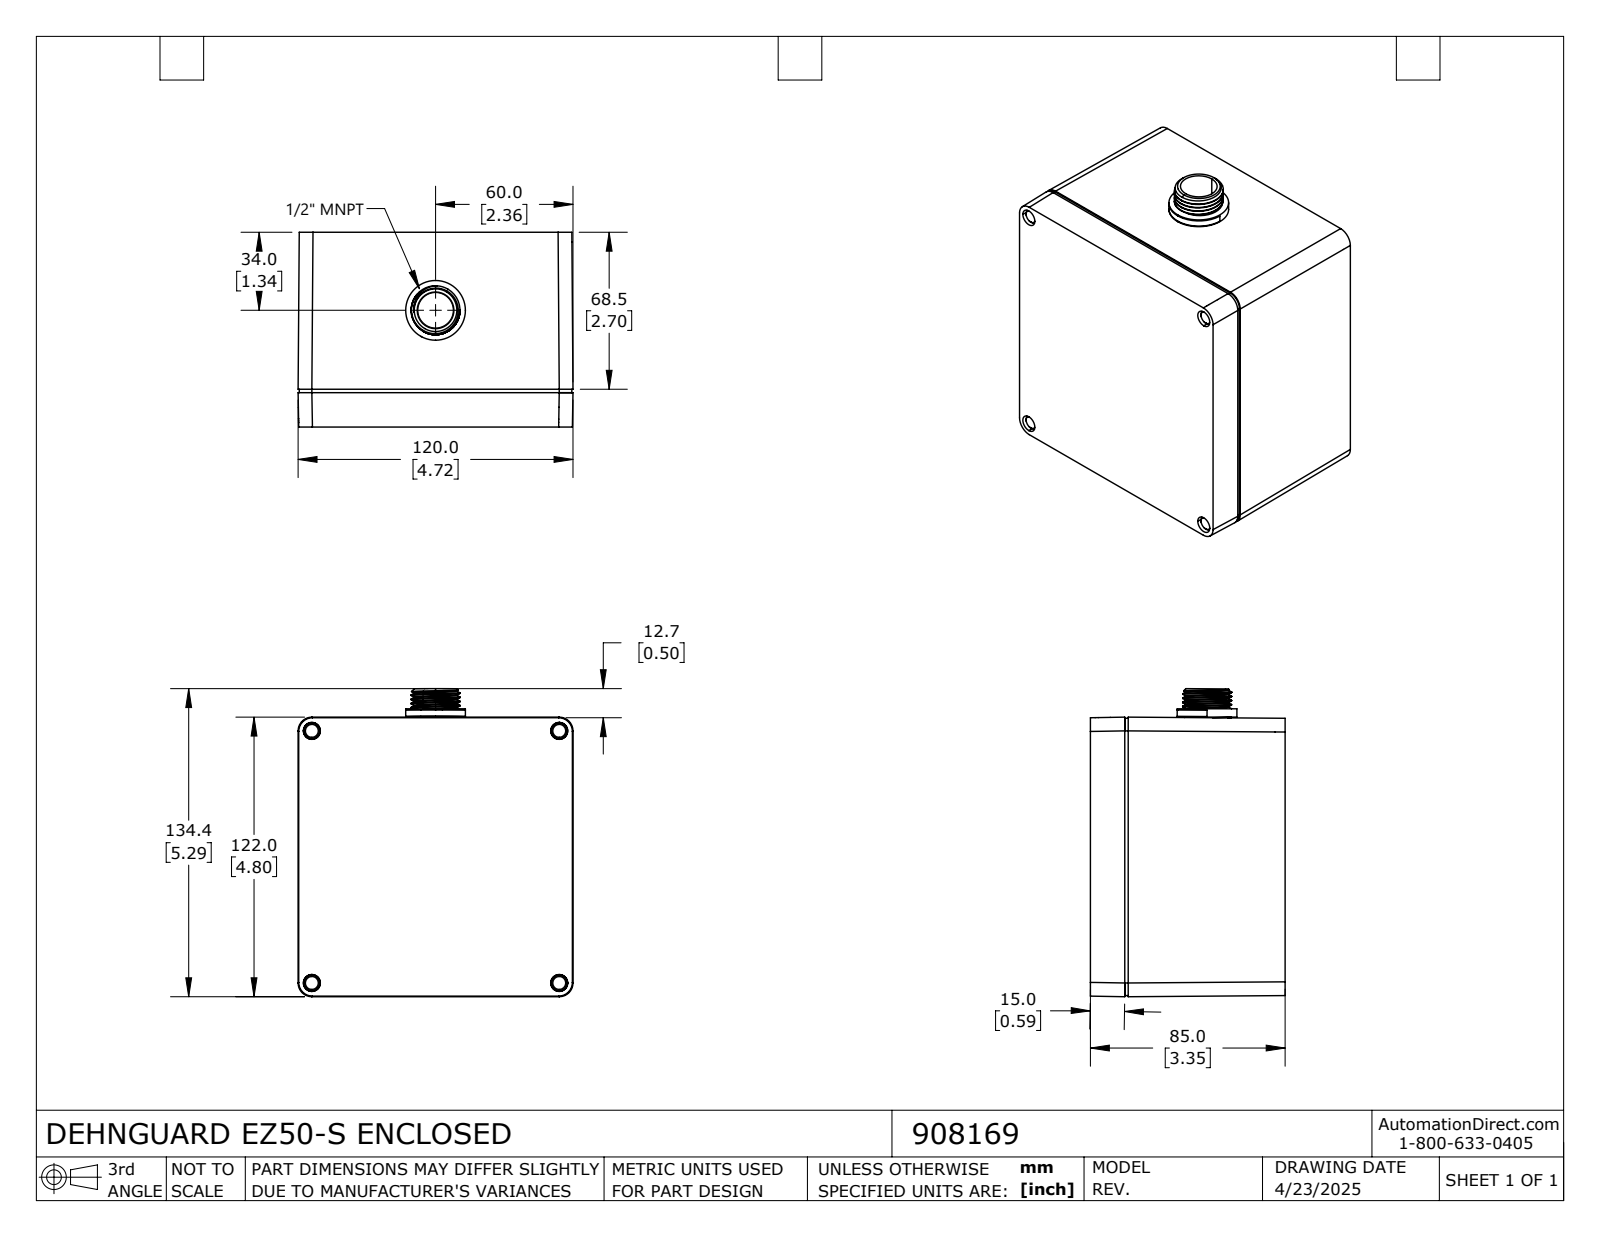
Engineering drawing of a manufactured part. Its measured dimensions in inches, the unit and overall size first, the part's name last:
Units: inches
Overall size (bounding box): 5.293 × 4.724 × 3.346
Round holes (diameter × count): ⌀0.165 ×4, ⌀0.315 ×4
Round bosses / shafts (diameter × count): ⌀0.276 ×6, ⌀0.113 ×4, ⌀1.166 ×1, ⌀1.125 ×1, ⌀1.026 ×1, ⌀0.84 ×1
Partial cylindrical surfaces — rounded edges, fillets, slot ends (radius × count): R0.004 ×12, R0.047 ×12, R0.236 ×8, R0.217 ×4, R0.02 ×3, R0.008 ×2, R0.016 ×2, R0.03 ×2
Main face-to-face distances: 0.118, 0.157, 3.346, 3.189, 3.228, 3.071, 0.12, 0.039, 0.37, 0.119
Hole centre spacings: 3.543, 4.331, 5.596
Volume: 32.85 in³ · Surface area: 295.3 in²
Bodies: 2 solids, 836 faces (588 planar, 173 cylindrical, 75 other)
Part name (STEP PRODUCT): 908169
STEP written by: SolidWorks 2024 (AUTOMOTIVE_DESIGN)
